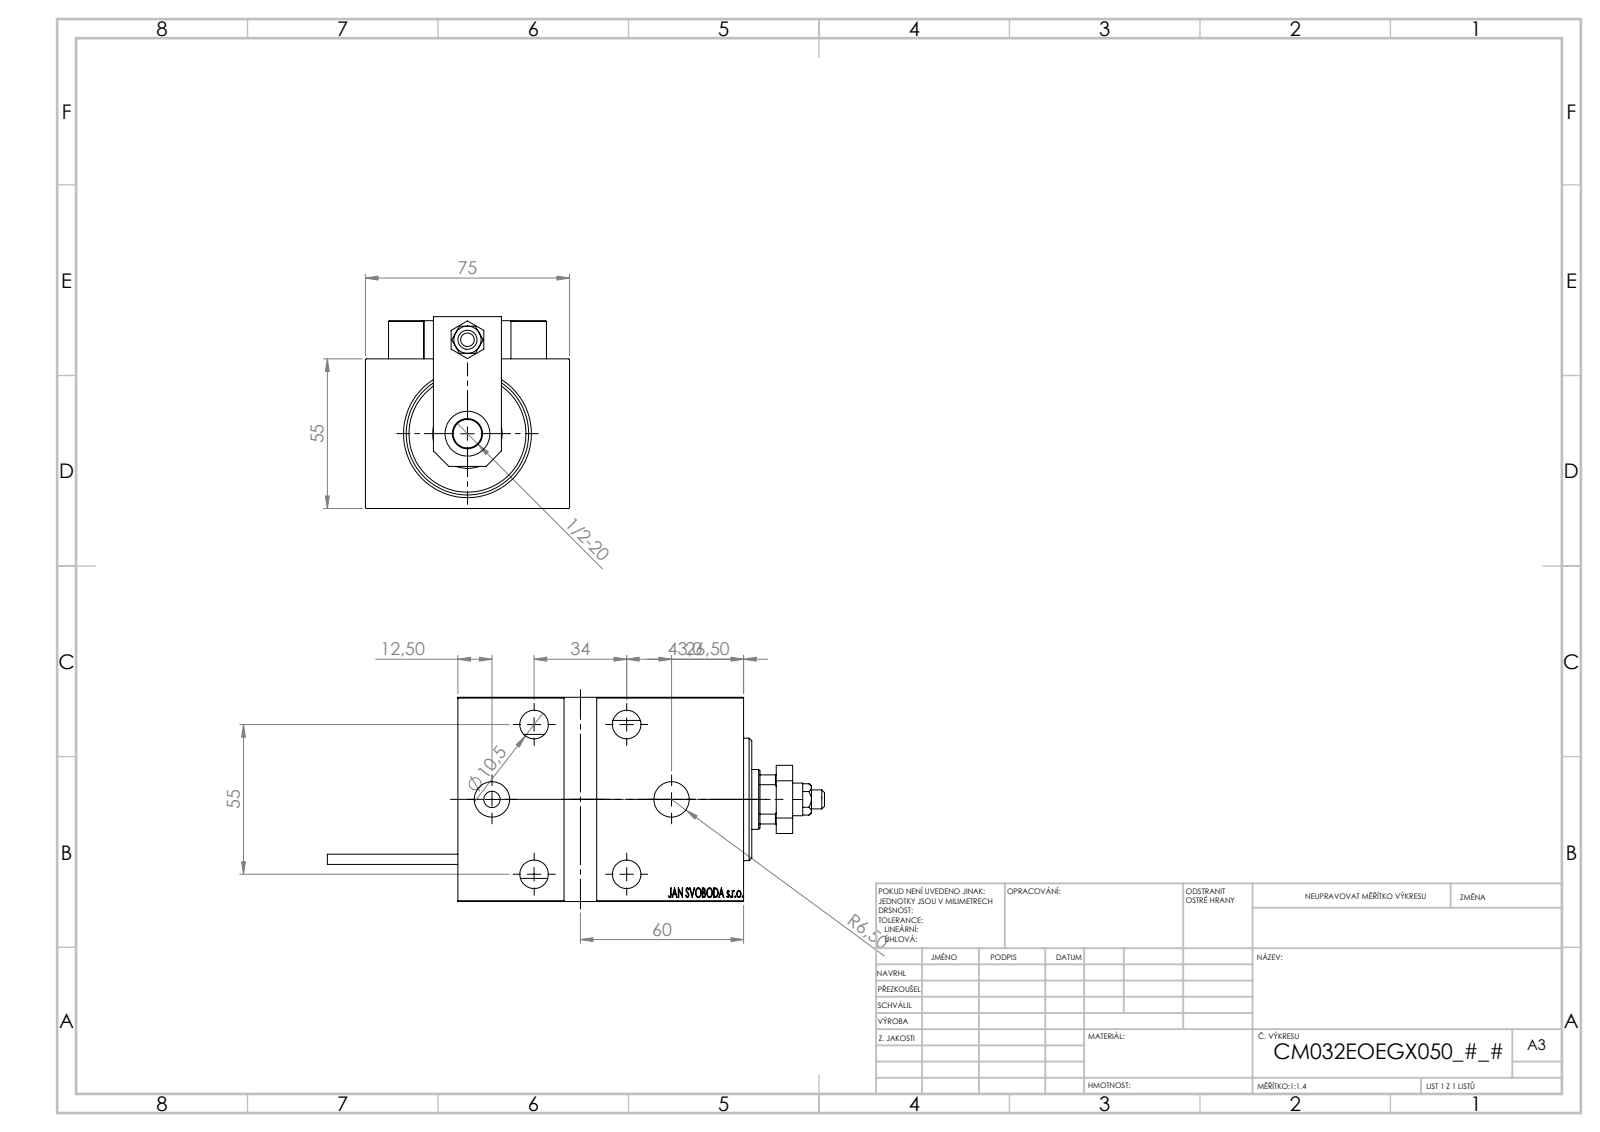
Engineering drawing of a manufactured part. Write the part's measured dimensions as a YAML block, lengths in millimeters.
part_name: "NUT_D10; Block; ZARAZKA; NUT_D12 (+7 more)"
step_written_by: "SolidWorks 2019 (CONFIG_CONTROL_DESIGN)"
units: millimeters
bodies: {solids: 24, faces: 1283, planar: 568, cylindrical: 174, other: 541}
overall_size: [182.7, 75, 70.5]
volume: 439904
surface_area: 95333
round_holes:
  - {diameter: 8, count: 5}
  - {diameter: 10.5, count: 5}
  - {diameter: 16.5, count: 5}
  - {diameter: 3.2, count: 4}
  - {diameter: 4, count: 4}
  - {diameter: 5, count: 2}
  - {diameter: 13, count: 2}
  - {diameter: 7, count: 1}
  - {diameter: 22, count: 1}
  - {diameter: 25.5, count: 1}
  - {diameter: 32, count: 1}
  - {diameter: 45, count: 1}
round_bosses_or_shafts:
  - {diameter: 5, count: 2}
  - {diameter: 3.8, count: 2}
  - {diameter: 34, count: 1}
  - {diameter: 13, count: 1}
  - {diameter: 11, count: 1}
  - {diameter: 6, count: 1}
partial_cylinders:
  - {radius: 0.3, count: 30}
  - {radius: 3, count: 2}
  - {radius: 10.5, count: 1}
face_to_face_distances: [55, 75, 10, 3, 14, 69, 105, 5, 12, 95]
hole_center_spacings: [11.37, 12.5, 20, 21.91, 28.9, 29.59, 29.69, 31.57]
